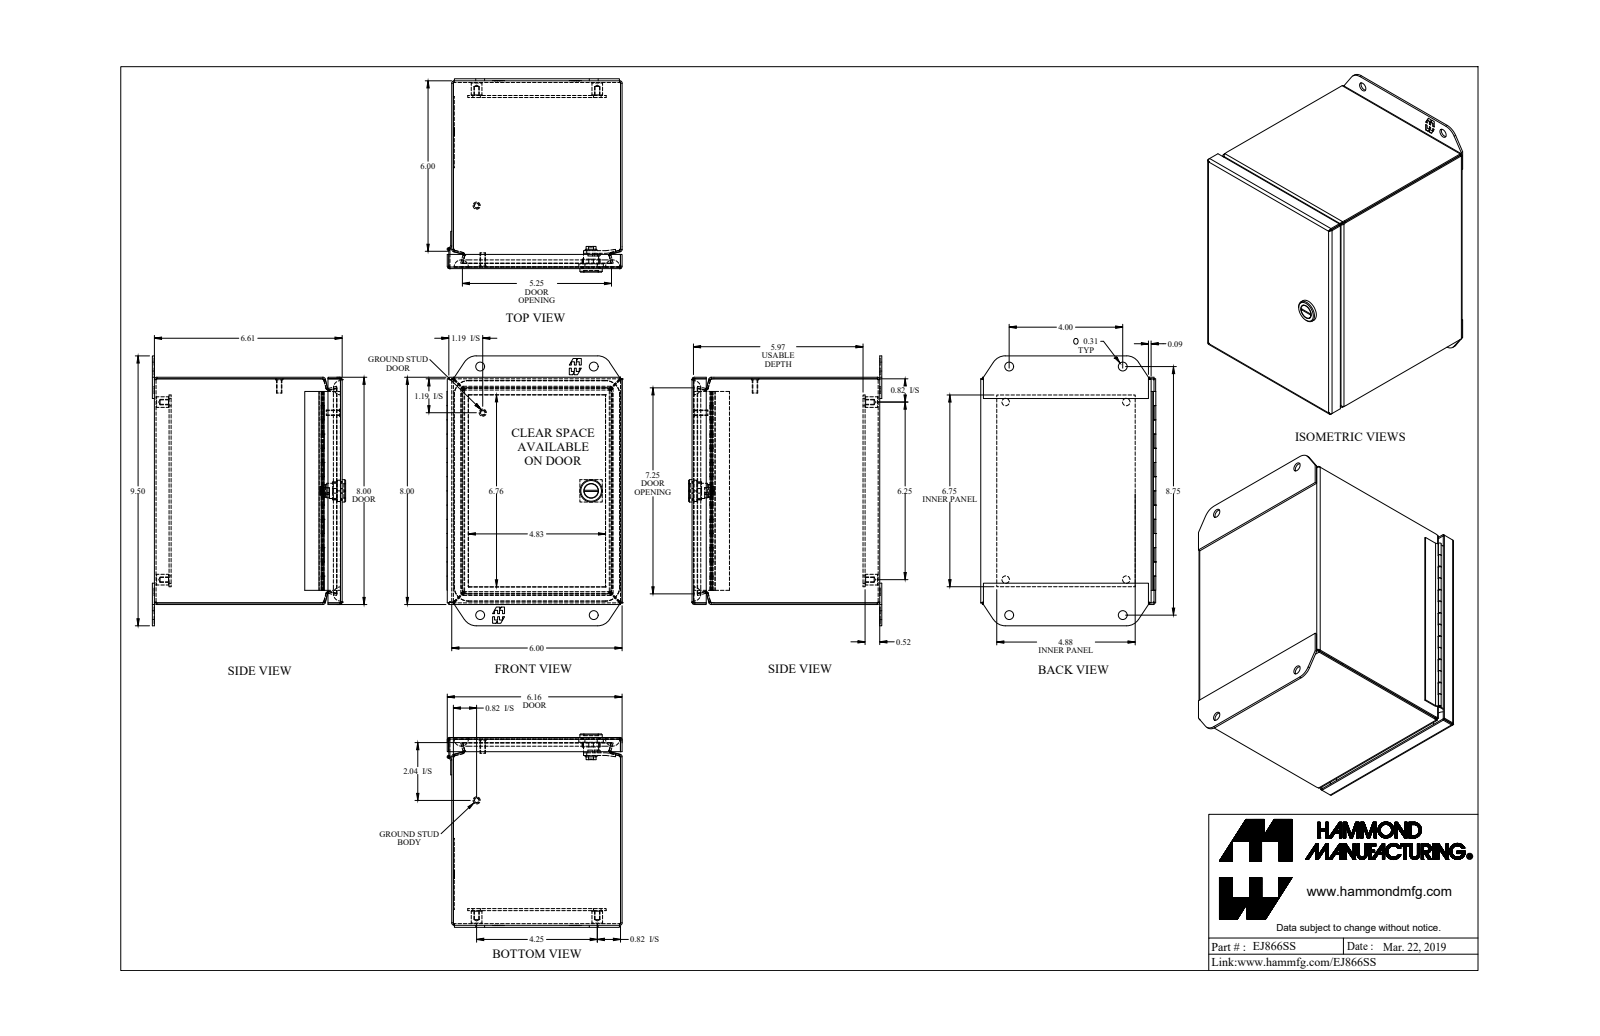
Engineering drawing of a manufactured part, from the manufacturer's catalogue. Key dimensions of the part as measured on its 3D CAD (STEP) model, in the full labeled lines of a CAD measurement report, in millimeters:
Part name (STEP PRODUCT): EJ866SS_Default
STEP written by: SolidWorks 2019 (CONFIG_CONTROL_DESIGN)
Units: millimetres
Bodies: 16 solids, 656 faces (370 planar, 190 cylindrical, 96 other)
Overall size (bounding box): 241.3 × 172.8 × 156.6
Volume: 381 300 mm³ · Surface area: 500 000 mm²
Round holes (diameter × count): ⌀4 ×4, ⌀6.7 ×4, ⌀8 ×4, ⌀1.3 ×1, ⌀13.1 ×1
Round bosses / shafts (diameter × count): ⌀9.5 ×4, ⌀6.4 ×2, ⌀4.8 ×2, ⌀20 ×1, ⌀13.6 ×1, ⌀12.6 ×1, ⌀11 ×1, ⌀2.5 ×1
Partial cylindrical surfaces — rounded edges, fillets, slot ends (radius × count): R0.7 ×16, R2.2 ×16, R7.1 ×12, R6.4 ×4, R12.7 ×4, R12.7 ×4, R1.5 ×2, R0.8 ×1
Main face-to-face distances: 1.4, 166.5, 151, 201.8, 1.8, 15, 149.5, 167.9, 152.4, 165
Hole centre spacings: 31.9, 109.5, 190.6, 217.4, 79.6, 101.6, 108, 111.2
